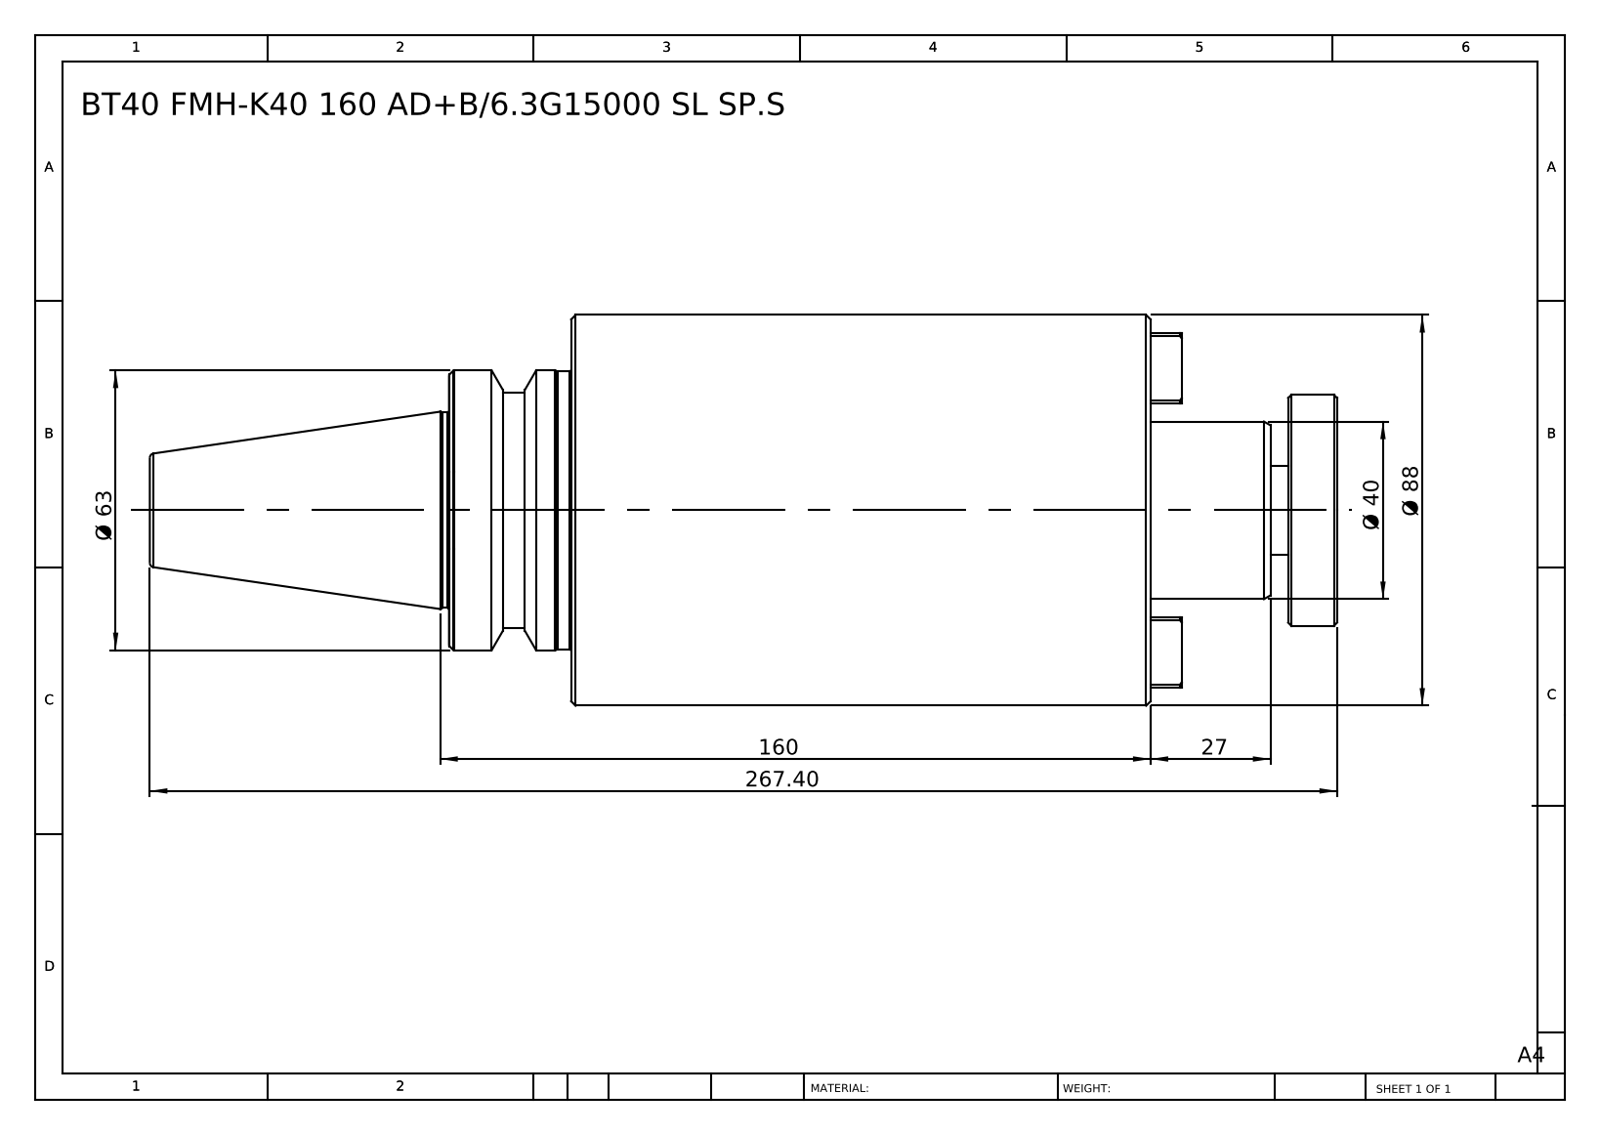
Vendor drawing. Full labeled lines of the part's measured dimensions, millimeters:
Part name (STEP PRODUCT): BT40 FMH40 160 AD-6.3G 15000 SL SP.S
STEP written by: SolidWorks 2014 (CONFIG_CONTROL_DESIGN)
Units: millimetres
Bodies: 1 solid, 93 faces (35 planar, 18 cylindrical, 40 other)
Overall size (bounding box): 267.4 × 88 × 88
Volume: 1 002 000 mm³ · Surface area: 70 367 mm²
Round bosses / shafts (diameter × count): ⌀88 ×1, ⌀63 ×1, ⌀62.5 ×1, ⌀53 ×1, ⌀52 ×1, ⌀44 ×1, ⌀40 ×1, ⌀20 ×1
Main face-to-face distances: 130.5, 42, 172.5, 11, 31, 161.5, 200, 189, 158, 27.5
